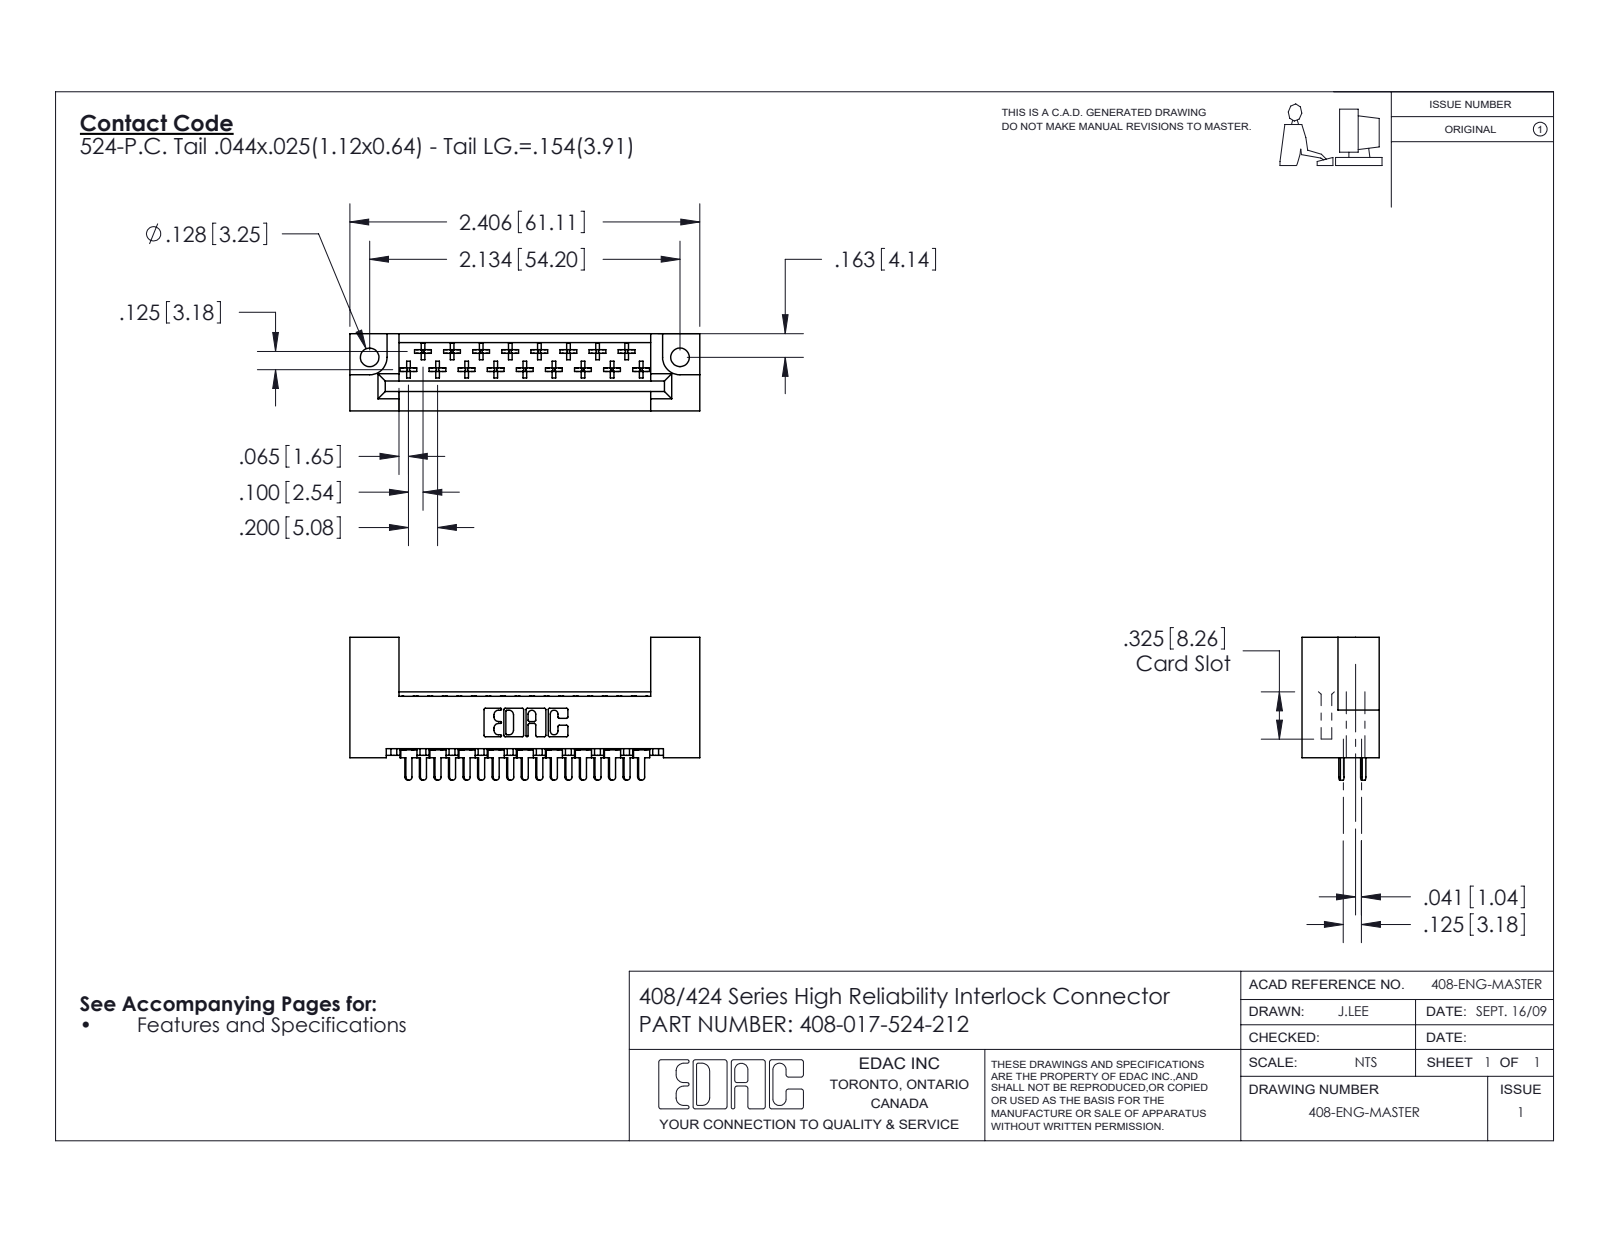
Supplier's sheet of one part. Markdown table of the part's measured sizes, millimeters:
| quantity | value |
| --- | --- |
| part name | 408-290-001_408-290-124 - Top; 408-290-001_408-290-124 - Bottom; 408 Part_017 - 2; 408-017-524-212 |
| STEP written by | SolidWorks 2016 (CONFIG_CONTROL_DESIGN) |
| units | millimeters |
| bodies | 18 solids, 1074 faces (803 planar, 203 cylindrical, 68 other) |
| overall size | 61.1 × 24.9 × 13.5 |
| volume | 8 240 mm³ |
| surface area | 8 755 mm² |
| round holes (diameter × count) | 3.3 × 2 |
| partial cylindrical surfaces (radius × count) | 0.3 × 102, 0.3 × 22, 0.5 × 19, 0.6 × 17, 0.2 × 6, 0.8 × 6, 0.7 × 3, 3 × 2 |
| main face-to-face distances | 13.5, 3.2, 0.6, 2.5, 0.6, 10.1, 8.3, 9.2, 1.8, 5.2 |
| hole center spacings | 54.2 |
